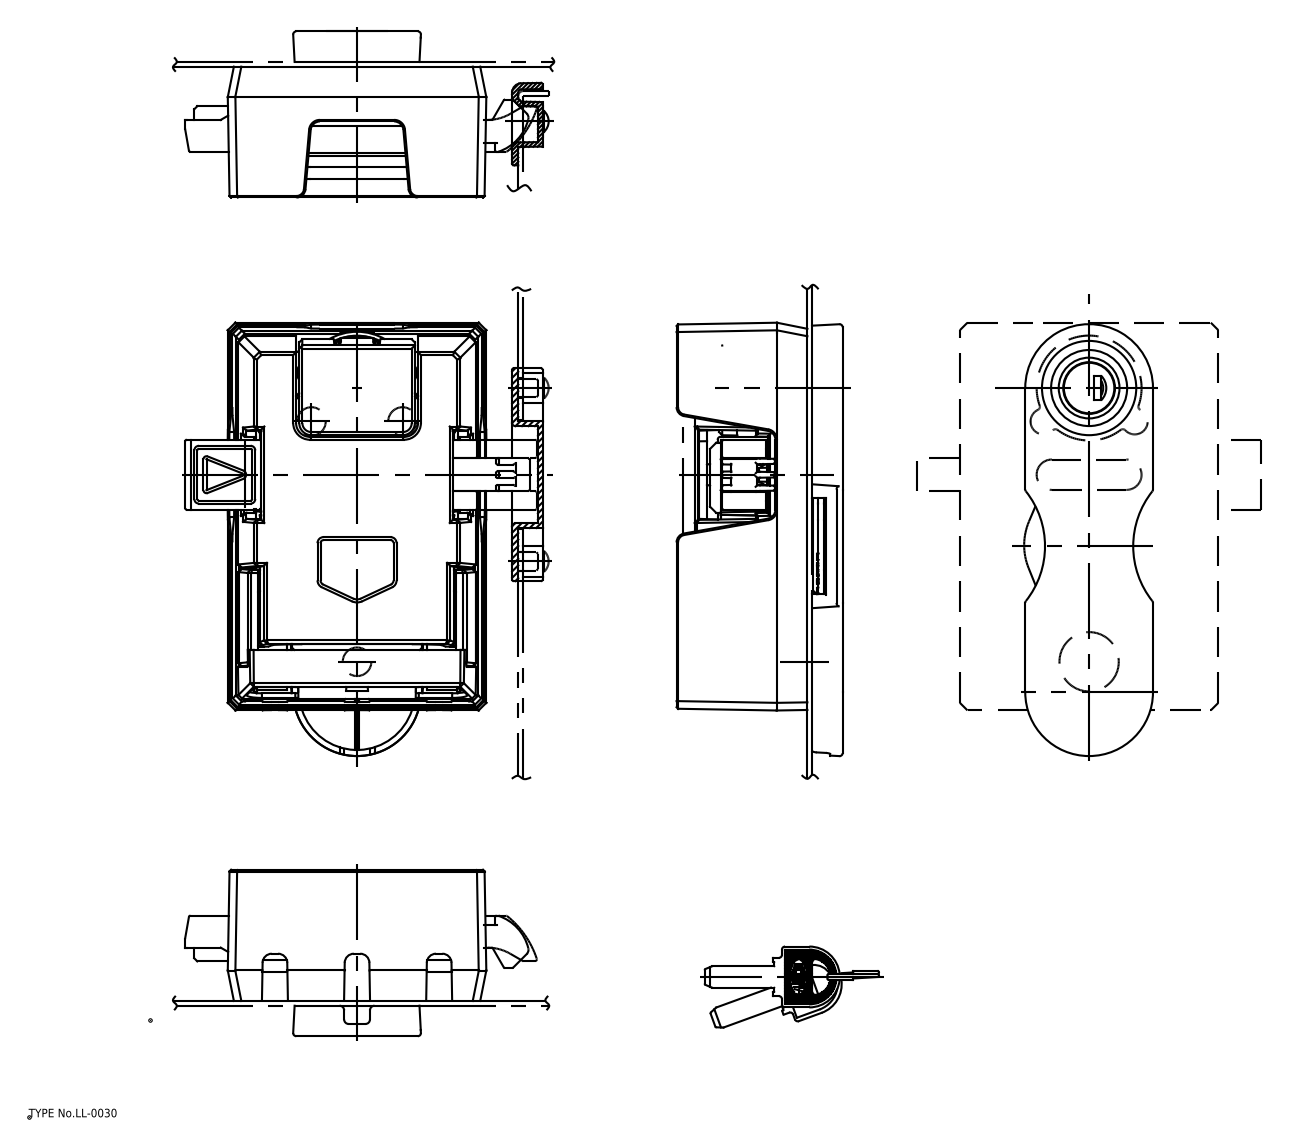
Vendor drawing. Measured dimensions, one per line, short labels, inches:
name: LL_0030_M1; LL_0030_M2; LL_0030_M3; LL_0030_M4 (+7 more)
written by: spGate 20.6.3 (****-****-****-****) (AUTOMOTIVE_DESIGN)
unit: in
bodies: 11 solids, 1621 faces (1032 planar, 375 cylindrical, 214 other)
size: 5.61 × 4.482 × 4.152
volume: 11.08 in³; area: 243.8 in²
holes: 3× ⌀0.142, 3× ⌀0.177, 2× ⌀0.165, 1× ⌀0.205, 1× ⌀0.276, 1× ⌀0.283, 1× ⌀0.315, 1× ⌀0.335, 1× ⌀0.484, 1× ⌀0.638, 1× ⌀0.669, 1× ⌀1.024
bosses: 3× ⌀0.37, 3× ⌀0.157, 2× ⌀0.748, 2× ⌀0.272, 2× ⌀0.217, 2× ⌀0.118, 1× ⌀1.339, 1× ⌀1.142
rounds: 84× R0.02, 74× R0.039, 18× R0.118, 10× R0.008, 9× R0.059, 8× R0.197, 6× R0.079, 6× R0.394
face distances: 0.079, 0.059, 0.433, 0.453, 0.039, 0.984, 1.476, 0.457, 0.492, 0.138
hole spacings: 0.732, 1.362, 1.551, 1.899, 2.173, 2.183, 2.492, 3.166
